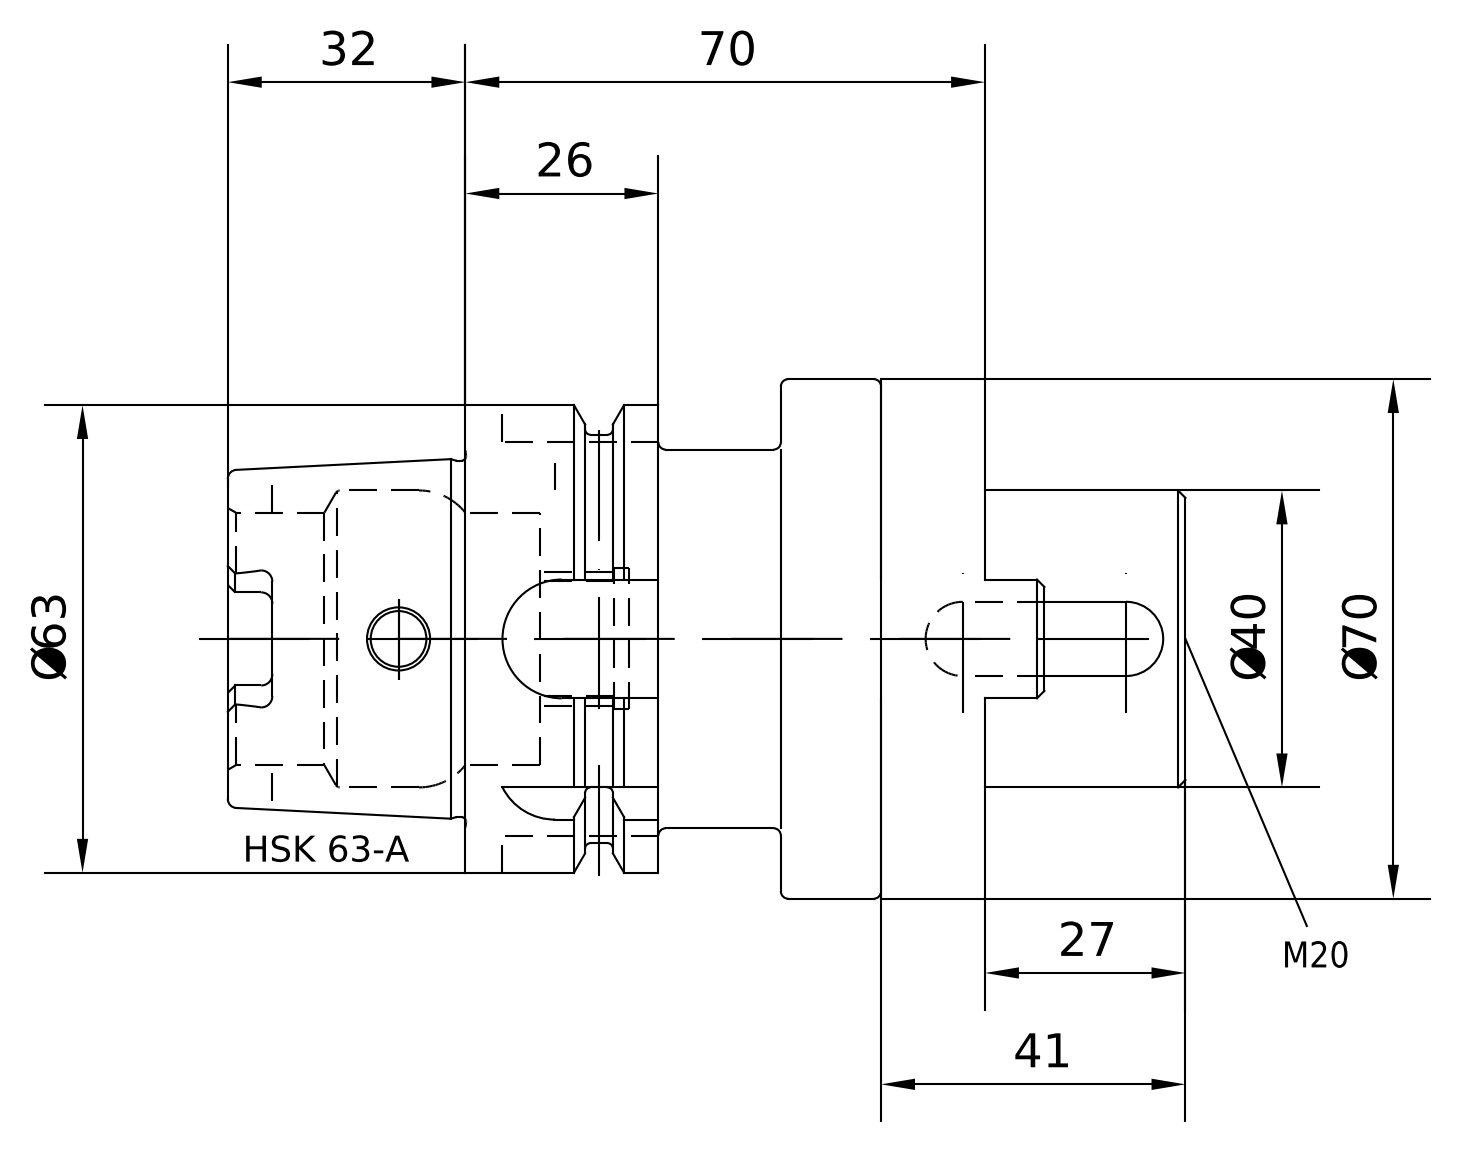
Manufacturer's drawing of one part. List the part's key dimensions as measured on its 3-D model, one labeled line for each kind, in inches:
Part name (STEP PRODUCT): A63-040-40; 85-200-40; A63-040-40_ASM
STEP written by: PRO/ENGINEER BY PARAMETRIC TECHNOLOGY CORPORATION, 2010430 (CONFIG_CONTROL_DESIGN)
Units: inches
Bodies: 2 solids, 272 faces (126 planar, 66 cylindrical, 80 other)
Overall size (bounding box): 5.079 × 2.756 × 2.756
Volume: 14.65 in³ · Surface area: 83.2 in²
Round holes (diameter × count): ⌀0.295 ×1, ⌀0.394 ×1, ⌀0.666 ×1, ⌀0.689 ×1, ⌀0.721 ×1, ⌀0.735 ×1, ⌀0.787 ×1, ⌀1.339 ×1, ⌀1.575 ×1, ⌀1.59 ×1, ⌀1.772 ×1
Round bosses / shafts (diameter × count): ⌀2.756 ×1, ⌀2.48 ×1, ⌀2.165 ×1, ⌀2.008 ×1, ⌀1.891 ×1, ⌀0.709 ×1
Partial cylindrical surfaces — rounded edges, fillets, slot ends (radius × count): R0.059 ×6, R0.118 ×4, R0.197 ×2, R0.315 ×1, R0.316 ×1, R0.317 ×1, R0.355 ×1
Main face-to-face distances: 0.551, 0.531, 1.083, 1.673, 2.205, 2.756, 3.819, 2.146, 1.614, 1.063
